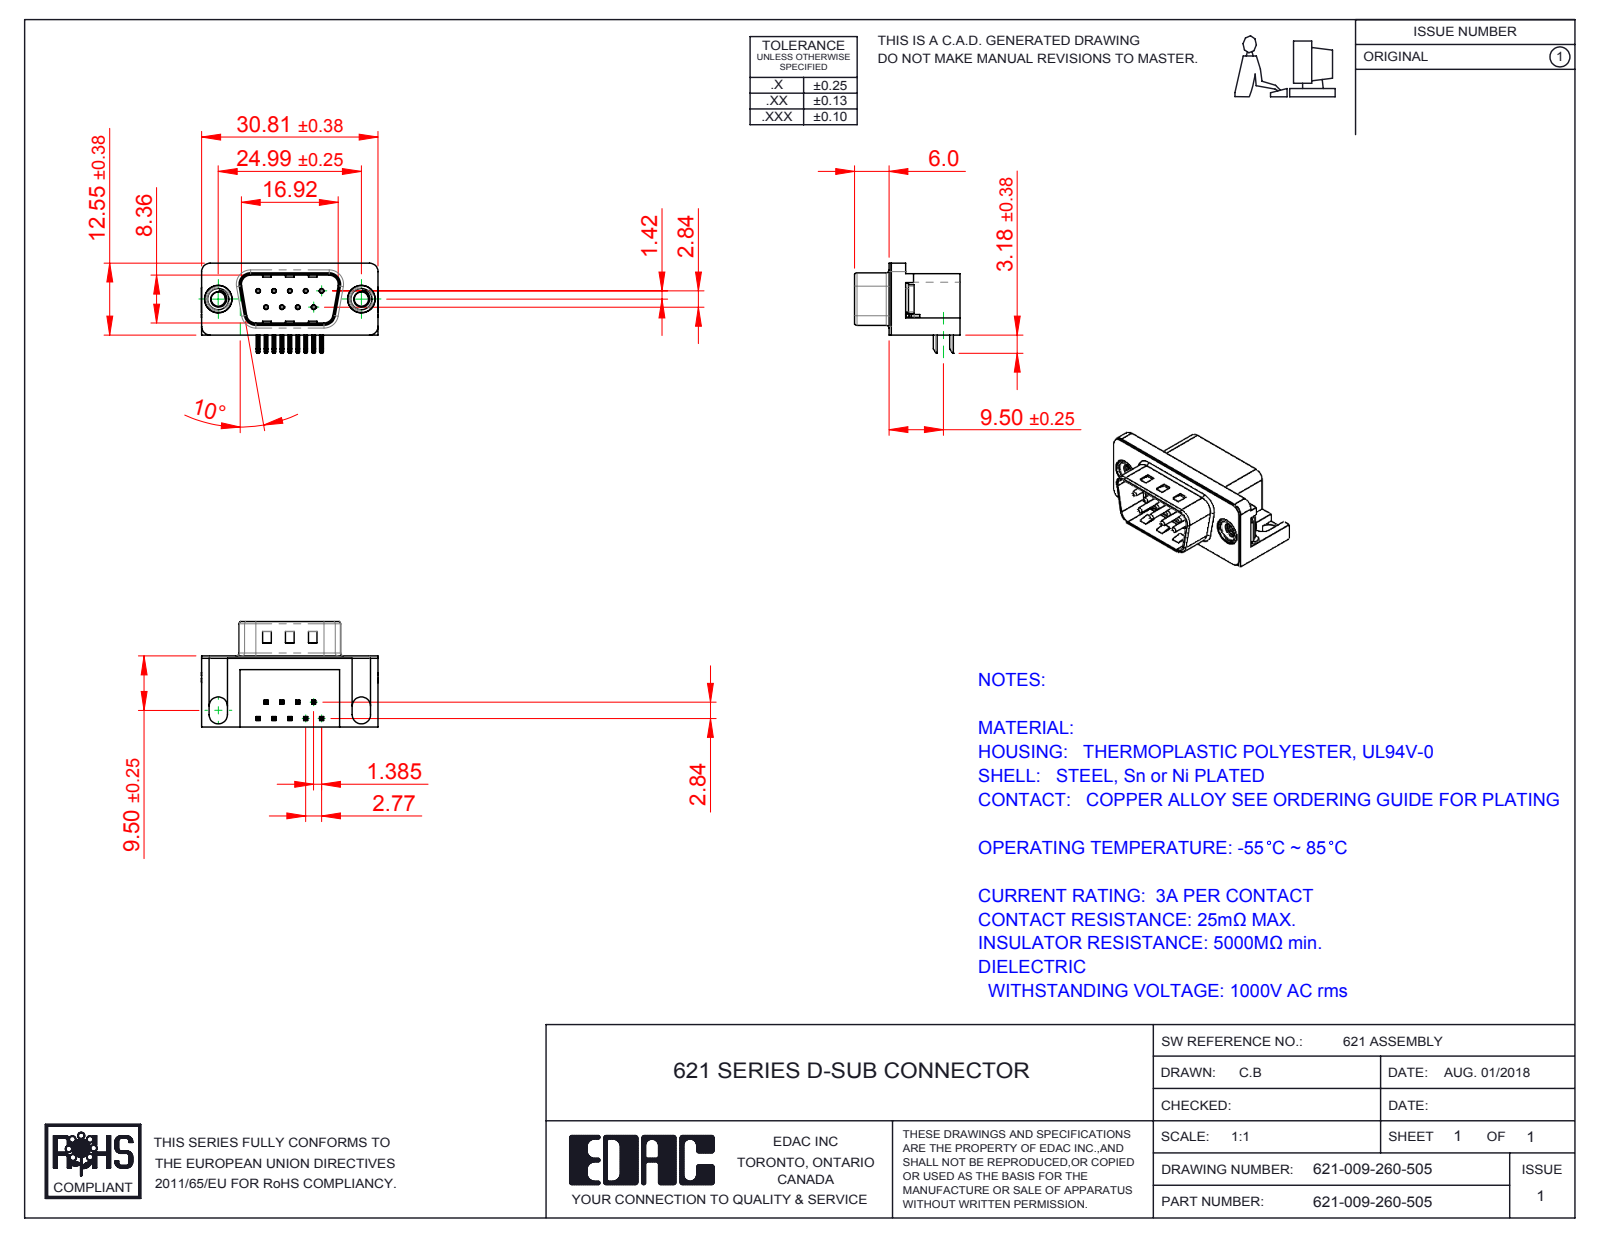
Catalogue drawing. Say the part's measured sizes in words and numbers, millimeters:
The part is named "621 M3 Threaded Rivet; 621-009-260-505; 621 Contact Top; 621 Housing_9 Socket (+3 more)". Its 3-D file was written by "SolidWorks 2016 (CONFIG_CONTROL_DESIGN)". It is 15 solids with 985 faces: 571 planar, 315 cylindrical and 99 other. Overall it measures 30.89 by 18.4 by 15.73 millimeters. Its volume is 3 204 cubic millimeters and its surface area 4 251 square millimeters. Round holes: 9 of diameter 0.35, 9 of diameter 0.8, 2 of diameter 2.5, 2 of diameter 4, 2 of diameter 4.8, 2 of diameter 5. Round bosses or shafts: 9 of diameter 0.75, 2 of diameter 4.9, 2 of diameter 4.75, 2 of diameter 3.9. Partial cylindrical surfaces (rounded edges, fillets, slot ends): 44 of radius 0.25, 18 of radius 0.12, 16 of radius 1, 9 of radius 0.5, 8 of radius 1.5, 8 of radius 1.6, 4 of radius 0.9, 4 of radius 2. The main face-to-face distances are 0.4, 12, 12.4, 10.35, 2.9, 9.5, 2.5, 2.1, 0.35, 10.7. The hole center spacings are 3.16, 2.77, 5.54, 5.03, 5.04, 8.31, 7.48, 7.49.
